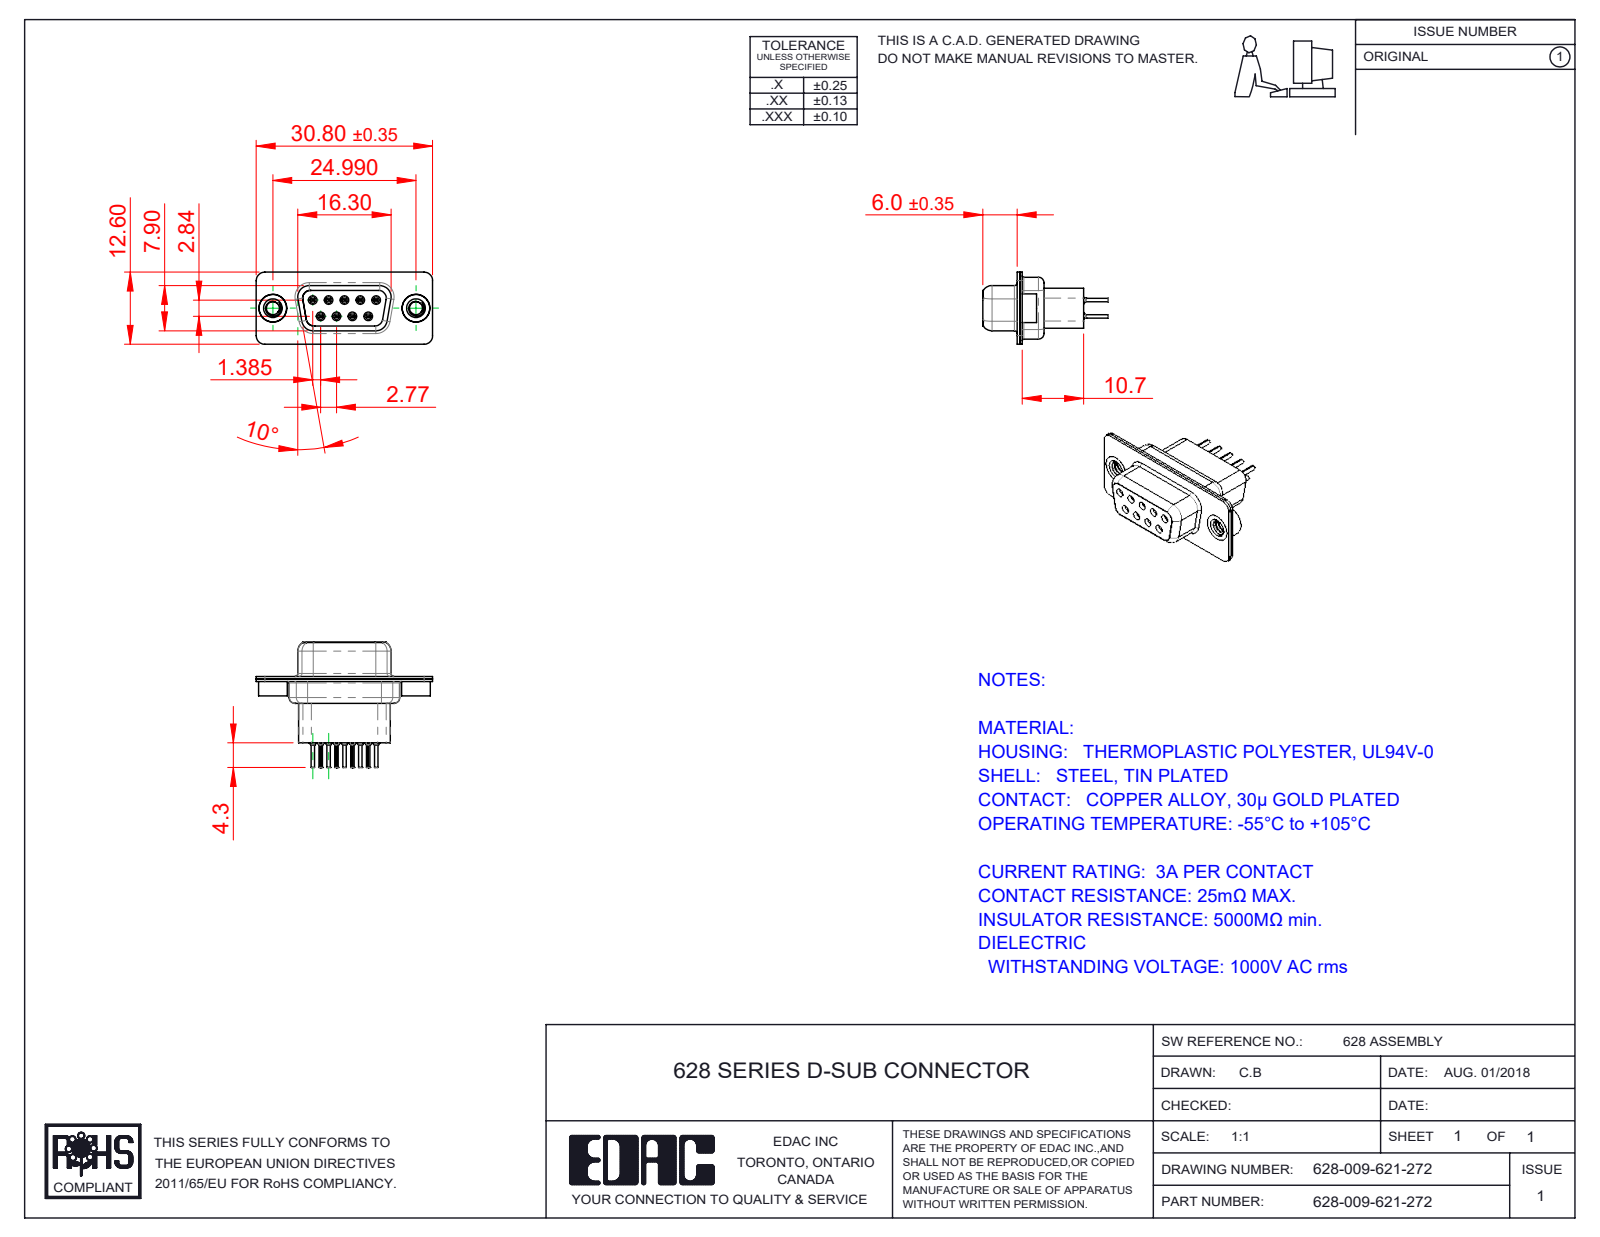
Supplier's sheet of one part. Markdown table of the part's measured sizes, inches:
| quantity | value |
| --- | --- |
| part name | 628 Shell Front_09 Contacts; 628 4-40 Threaded Rivet; 628 Housing_09 HP; 628 Shell Rear_09 Contacts (+3 more) |
| STEP written by | SolidWorks 2020 (CONFIG_CONTROL_DESIGN) |
| units | inches |
| bodies | 14 solids, 1382 faces (346 planar, 432 cylindrical, 604 other) |
| overall size | 1.213 × 0.862 × 0.496 |
| volume | 0.136 in³ |
| surface area | 8.252 in² |
| round holes (diameter × count) | 0.008 × 9, 0.031 × 9, 0.035 × 9, 0.043 × 9, 0.063 × 9, 0.067 × 5, 0.089 × 2, 0.157 × 2, 0.159 × 2, 0.191 × 2 |
| round bosses / shafts (diameter × count) | 0.079 × 9, 0.059 × 9, 0.047 × 9, 0.024 × 9, 0.197 × 2, 0.195 × 2, 0.189 × 2 |
| partial cylindrical surfaces (radius × count) | 0.004 × 18, 0.059 × 17, 0.079 × 12, 0.011 × 9, 0.053 × 6, 0.01 × 4, 0.02 × 4, 0.024 × 4 |
| main face-to-face distances | 0.018, 0.016, 0.035, 0.335, 0.26, 0.075, 0.055, 0.276, 0.421, 0.02 |
| hole center spacings | 0.124, 0.109, 0.218, 0.198, 0.198, 0.327, 0.294, 0.295 |
